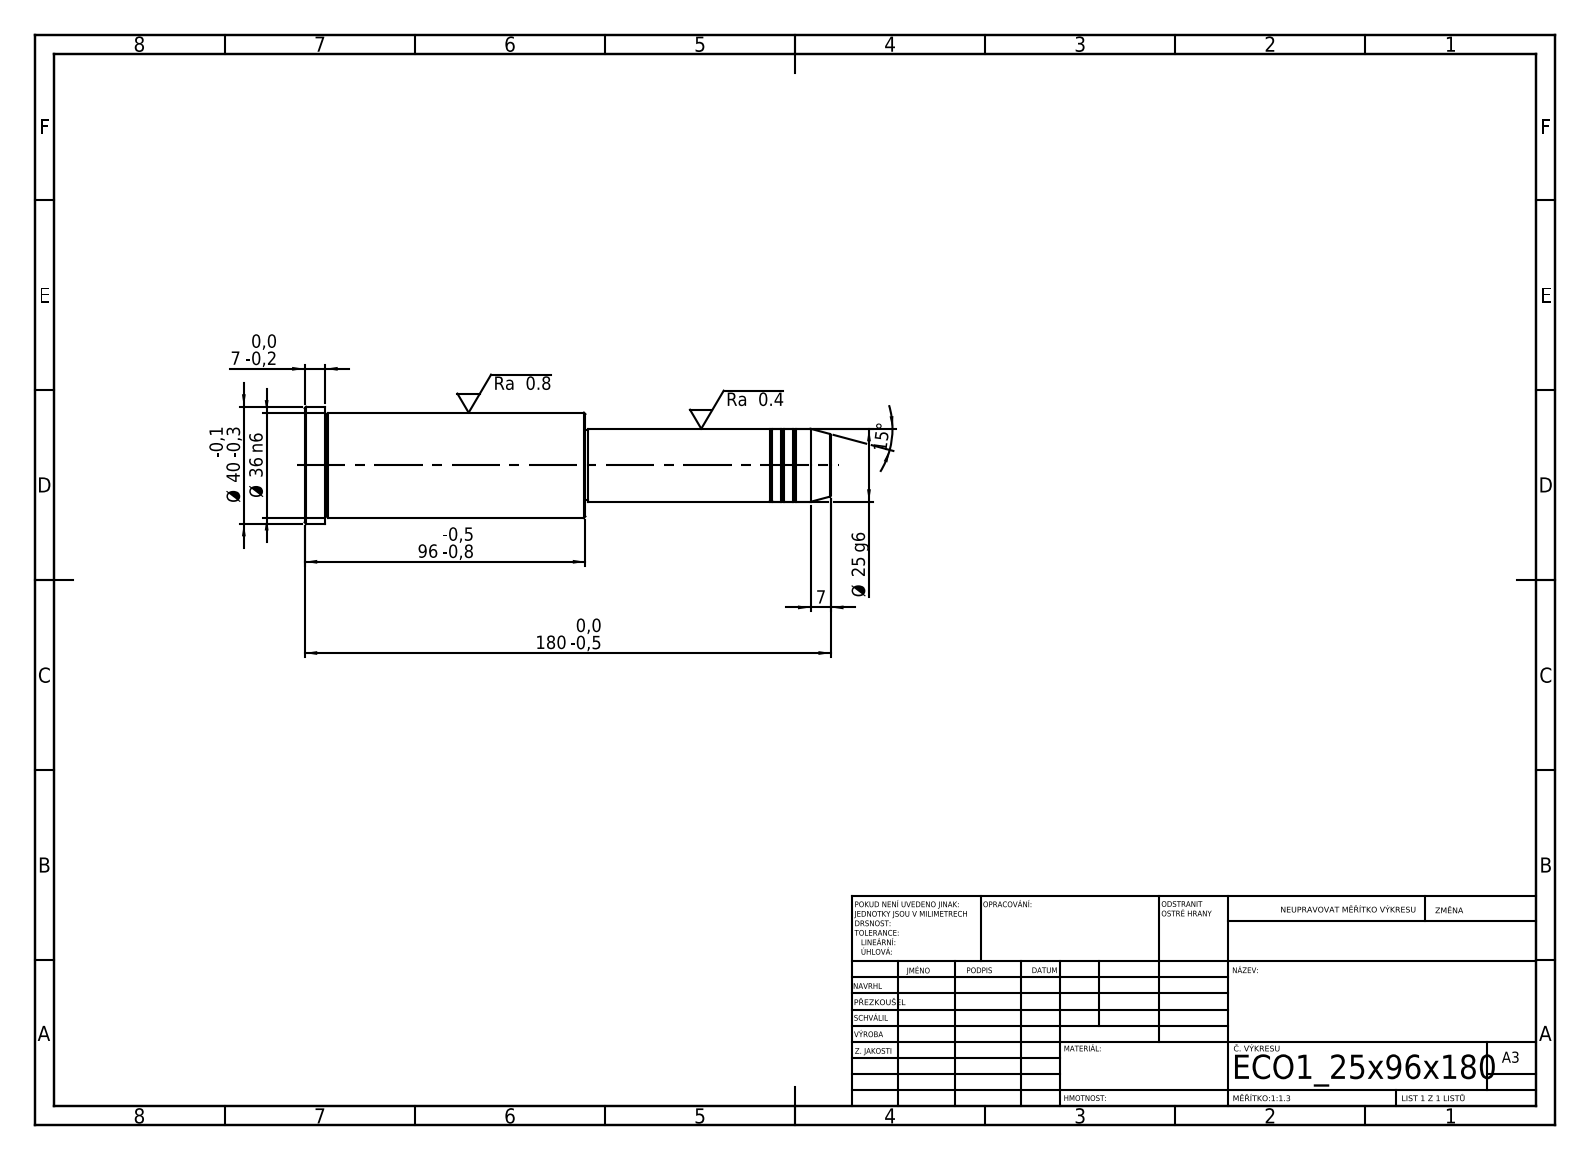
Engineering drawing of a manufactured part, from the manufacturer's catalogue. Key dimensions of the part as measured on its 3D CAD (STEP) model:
STEP written by: SolidWorks 2019 (CONFIG_CONTROL_DESIGN)
Units: millimetres
Bodies: 1 solid, 43 faces (5 planar, 14 cylindrical, 24 other)
Overall size (bounding box): 180 × 40 × 40
Volume: 139 926 mm³ · Surface area: 20 078 mm²
Round bosses / shafts (diameter × count): ⌀40 ×1, ⌀36 ×1, ⌀25 ×1, ⌀24 ×1
Main face-to-face distances: 96, 84, 180, 173, 89, 7, 83, 1, 90, 97
